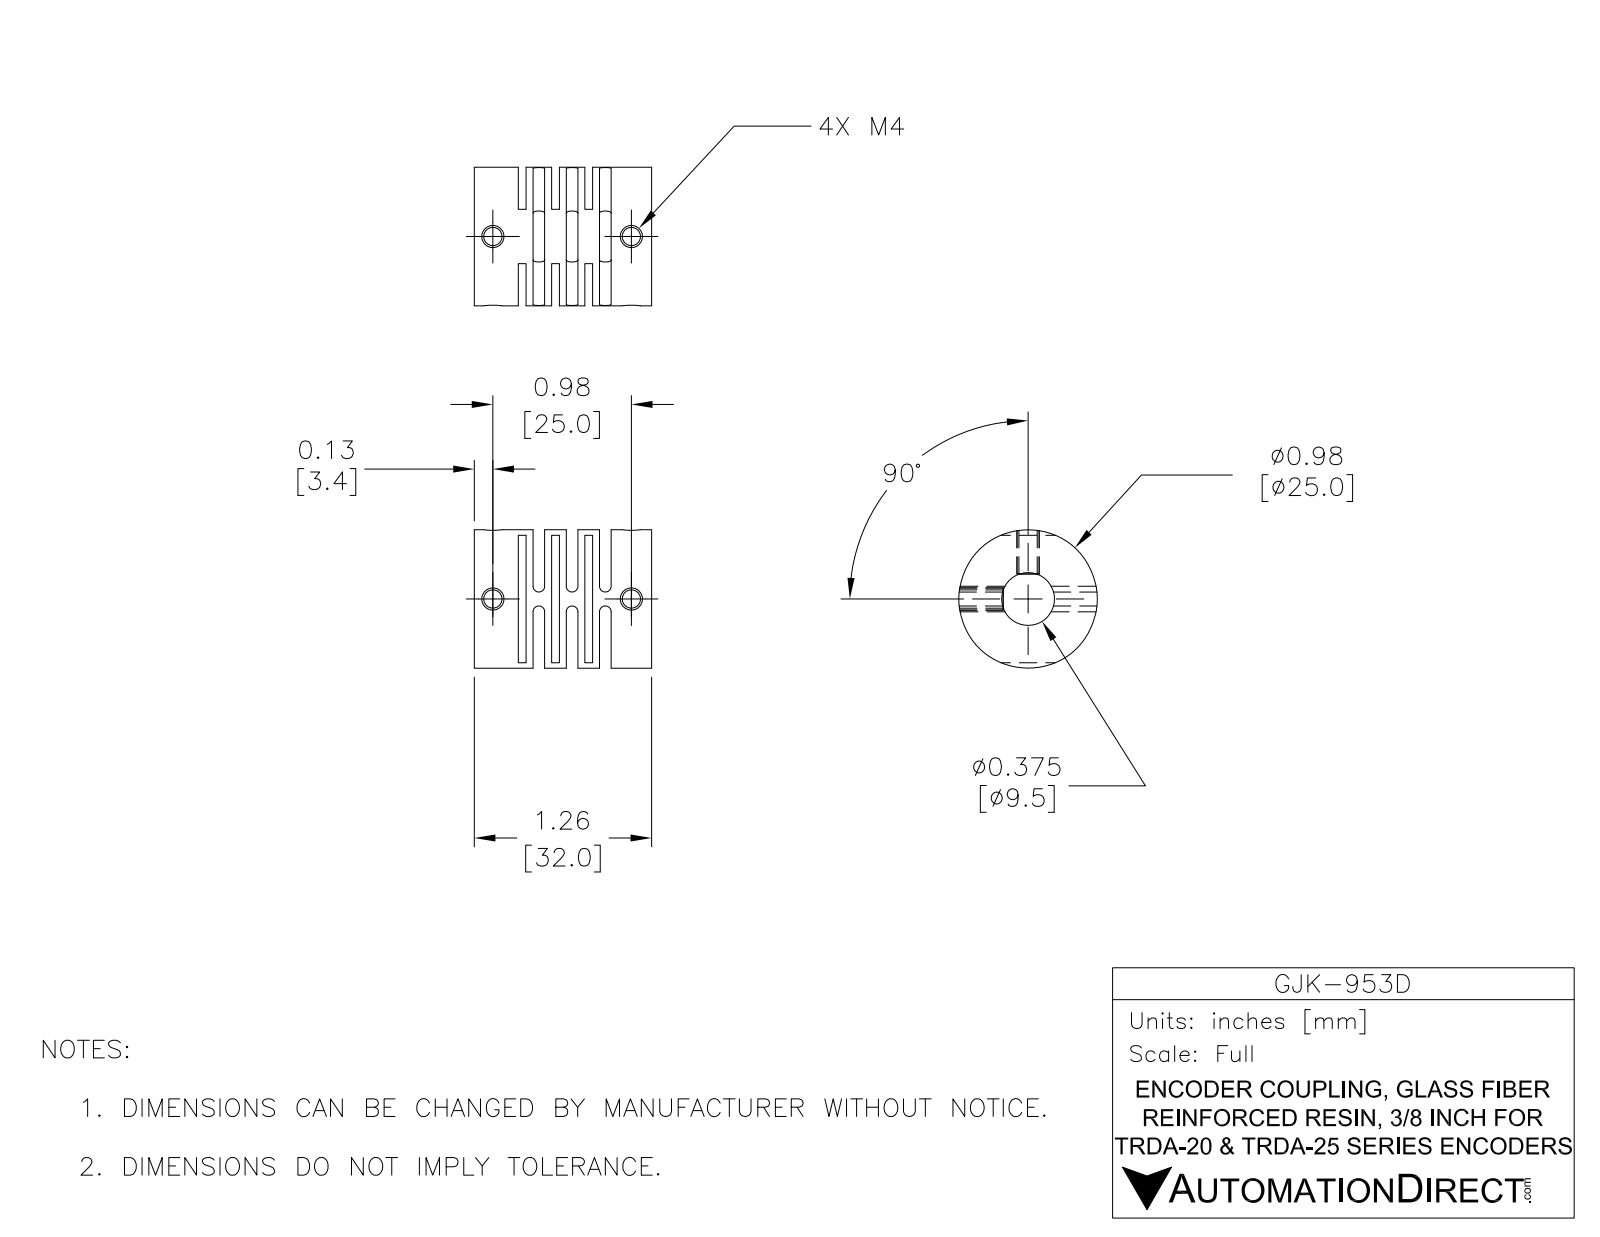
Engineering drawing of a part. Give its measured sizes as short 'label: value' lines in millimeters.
name: GJK-953D
written by: SolidWorks 2016 (AUTOMOTIVE_DESIGN)
unit: mm
bodies: 1 solid, 154 faces (102 planar, 20 cylindrical, 32 other)
size: 32 × 25 × 25
volume: 9 202 mm³; area: 10 073 mm²
holes: 4× ⌀3.5, 1× ⌀9.53
bosses: 1× ⌀25
face distances: 2.3, 4.6, 6.9, 9.2, 1.3, 1, 3.6, 3.3, 5.9, 11.5
hole spacings: 25
